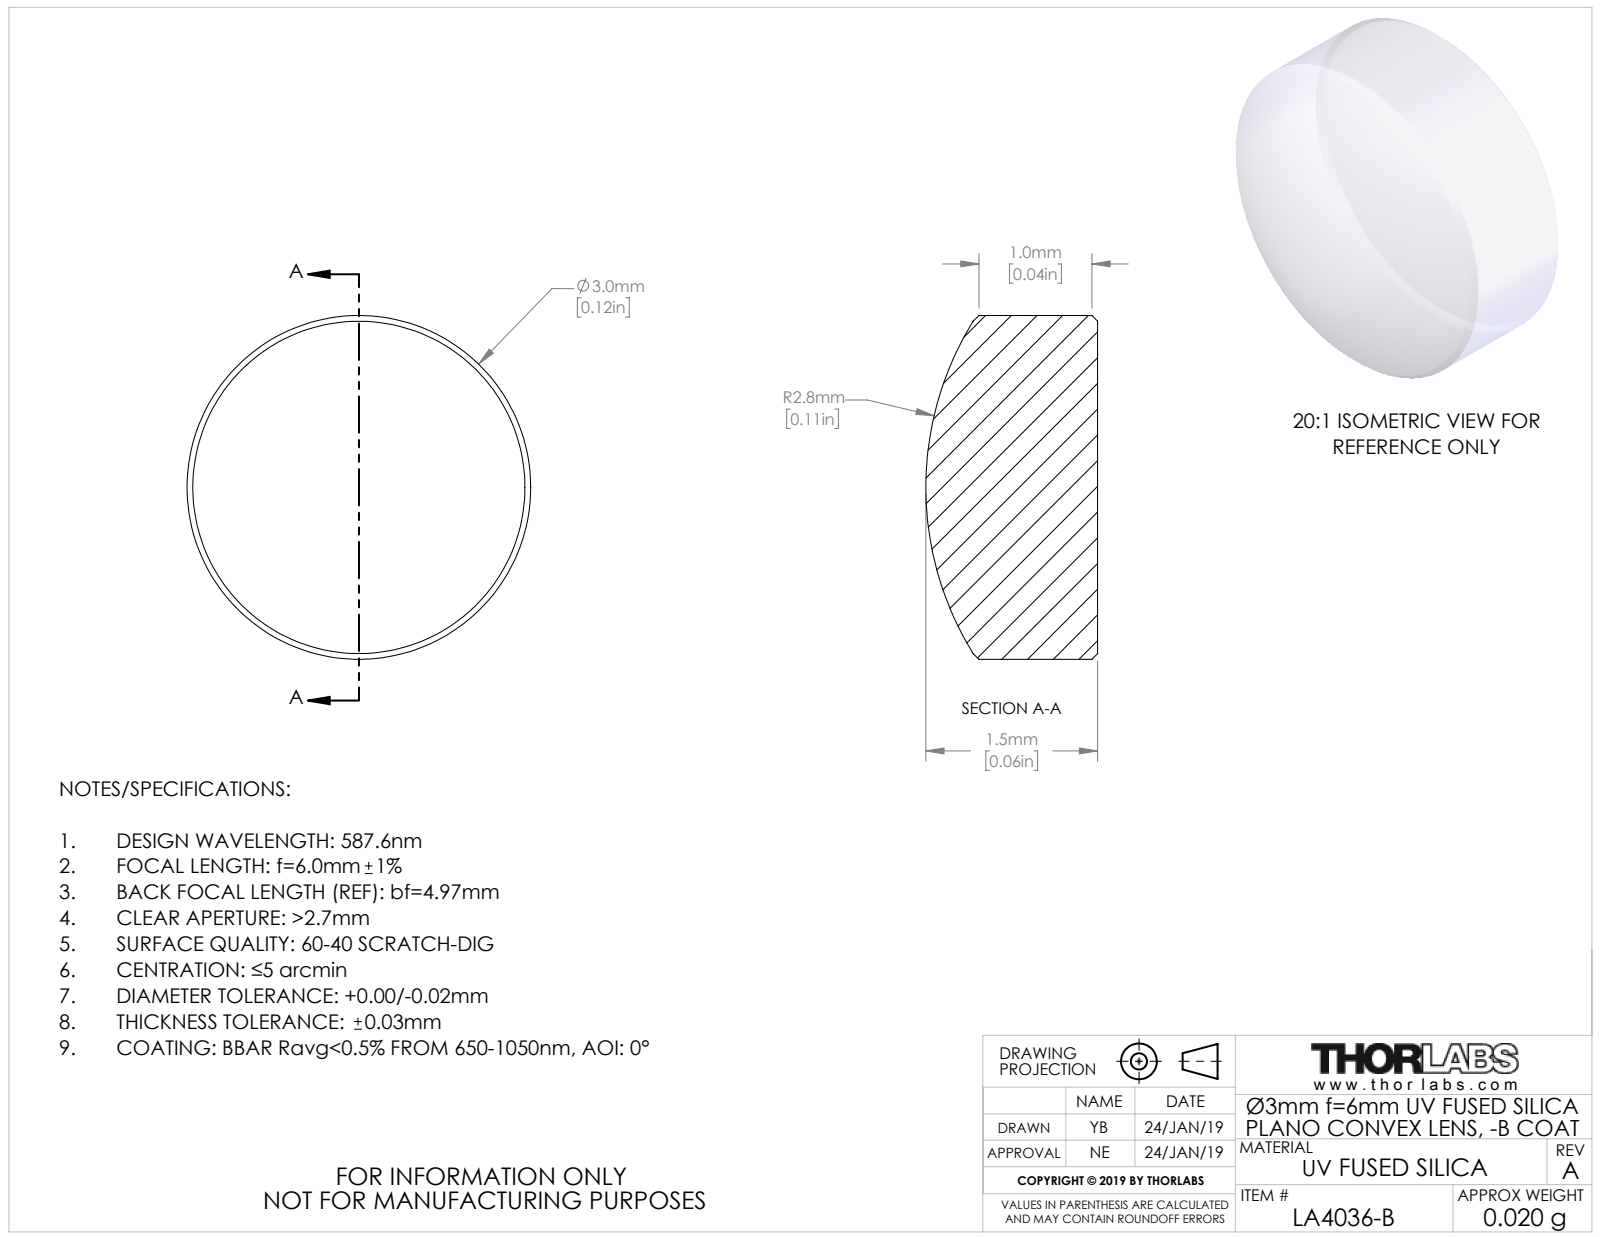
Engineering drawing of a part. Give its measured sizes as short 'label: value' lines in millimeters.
name: TTN162816-E0W
written by: SolidWorks 2018 (CONFIG_CONTROL_DESIGN)
unit: mm
bodies: 1 solid, 9 faces (1 planar, 2 cylindrical, 6 other)
size: 3 × 3 × 1.5
volume: 9 mm³; area: 24 mm²
bosses: 1× ⌀3
